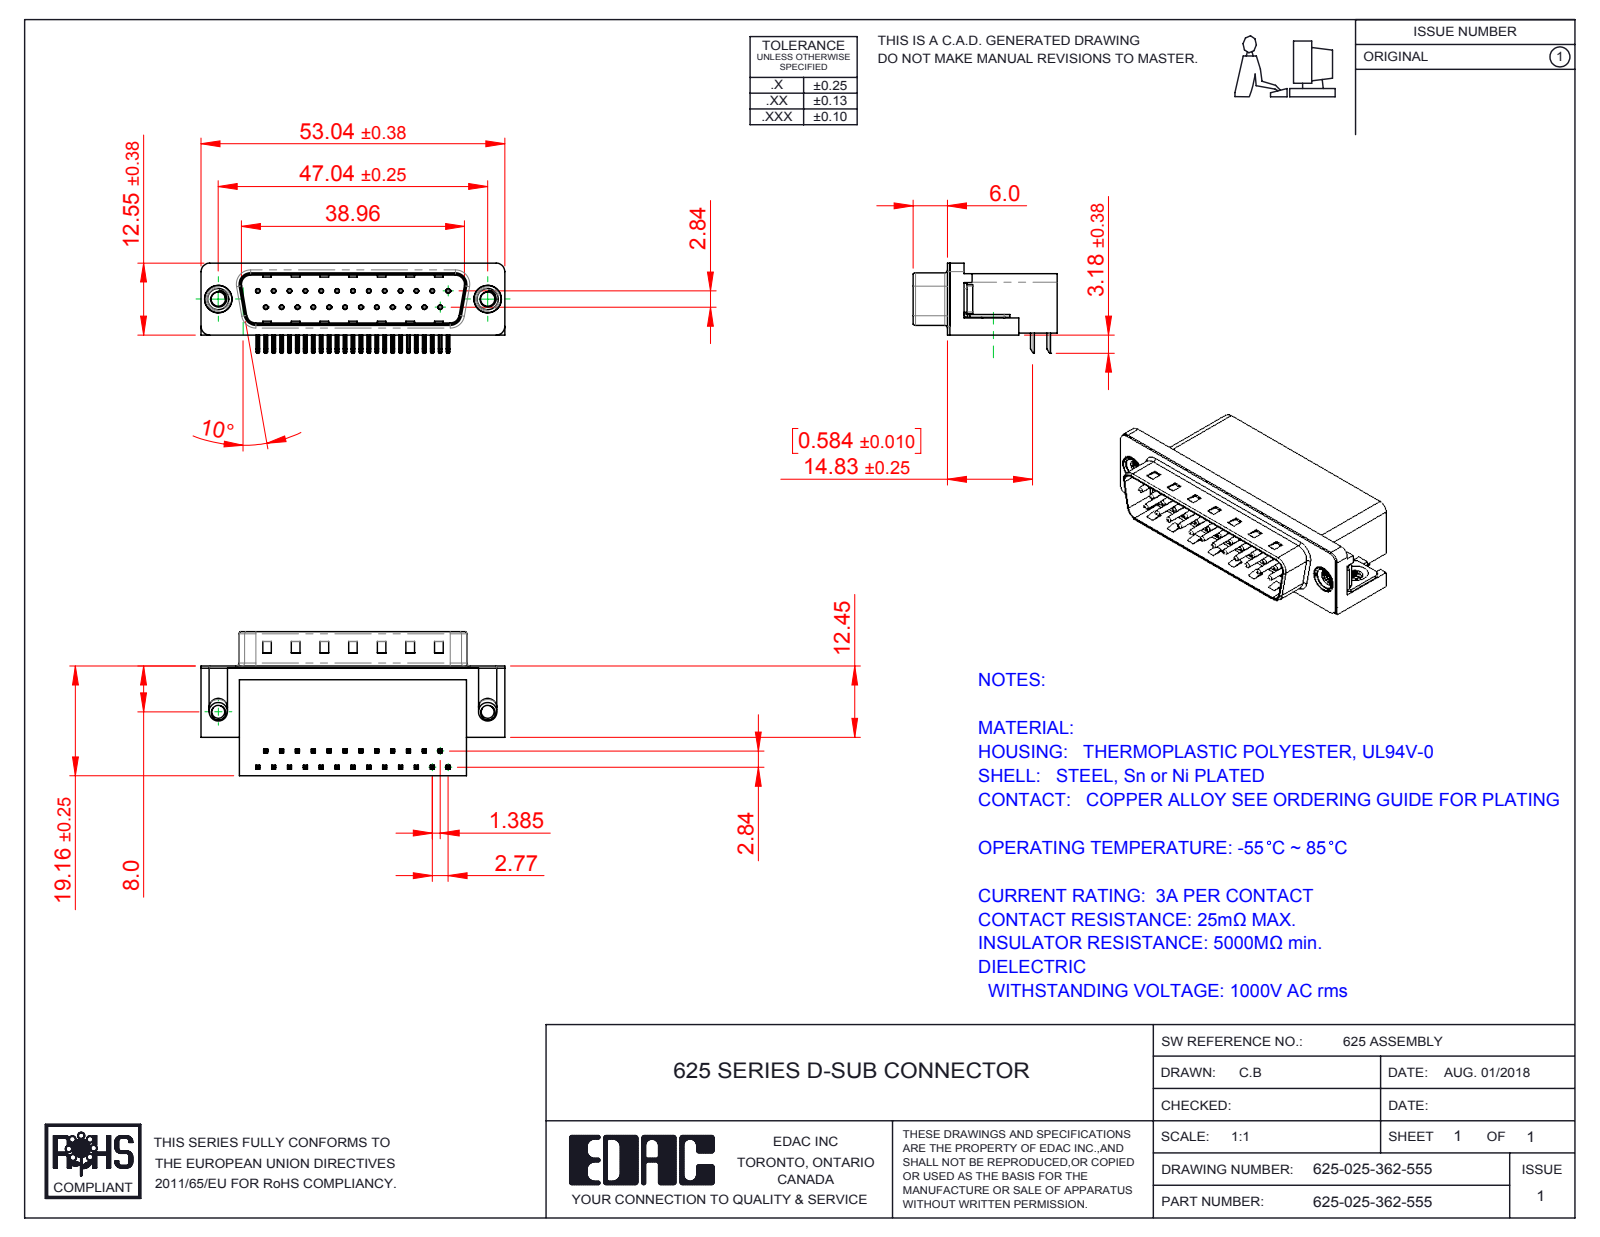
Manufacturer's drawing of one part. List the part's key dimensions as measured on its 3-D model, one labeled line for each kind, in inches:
Part name (STEP PRODUCT): 625 4-40 Threaded Board Mount; 625 Contact Bottom; 625 M3 Threaded Rivet; 625-025-362-555 (+3 more)
STEP written by: SolidWorks 2016 (CONFIG_CONTROL_DESIGN)
Units: inches
Bodies: 31 solids, 2297 faces (1407 planar, 677 cylindrical, 213 other)
Overall size (bounding box): 2.088 × 0.991 × 0.619
Volume: 0.56 in³ · Surface area: 13.86 in²
Round holes (diameter × count): ⌀0.014 ×25, ⌀0.031 ×25, ⌀0.089 ×2, ⌀0.098 ×2, ⌀0.157 ×2, ⌀0.189 ×2, ⌀0.197 ×2
Round bosses / shafts (diameter × count): ⌀0.03 ×25, ⌀0.193 ×2, ⌀0.187 ×2, ⌀0.154 ×2, ⌀0.128 ×2
Partial cylindrical surfaces — rounded edges, fillets, slot ends (radius × count): R0.01 ×108, R0.005 ×50, R0.039 ×16, R0.02 ×9, R0.063 ×8, R0.059 ×7, R0.035 ×4, R0.079 ×4
Main face-to-face distances: 0.016, 0.407, 0.739, 0.083, 0.345, 0.412, 0.428, 0.067, 0.754, 0.398
Hole centre spacings: 0.124, 0.109, 0.436, 0.218, 0.327, 0.198, 0.545, 0.294
